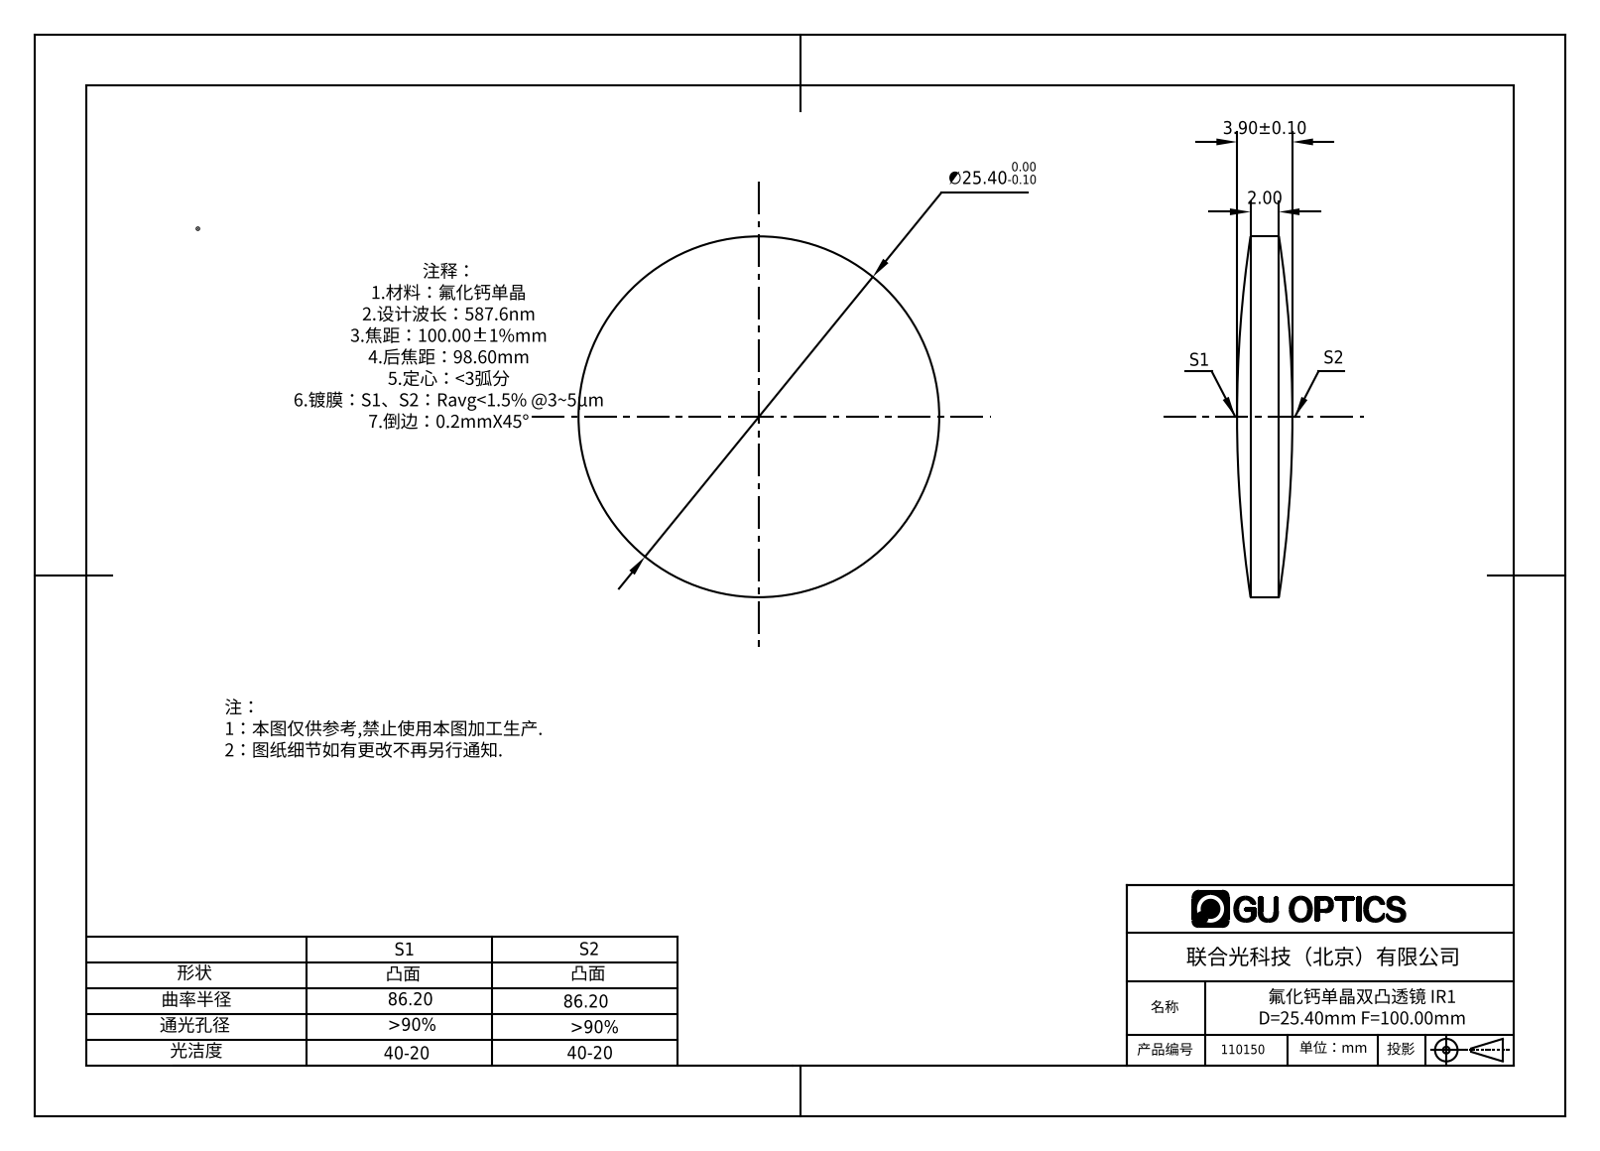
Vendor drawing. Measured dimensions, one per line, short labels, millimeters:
name: 110142
written by: SolidWorks 2016 (CONFIG_CONTROL_DESIGN)
unit: mm
bodies: 1 solid, 6 faces (0 planar, 0 cylindrical, 6 other)
size: 25.41 × 25.41 × 3.9
volume: 1 496 mm³; area: 1 179 mm²
